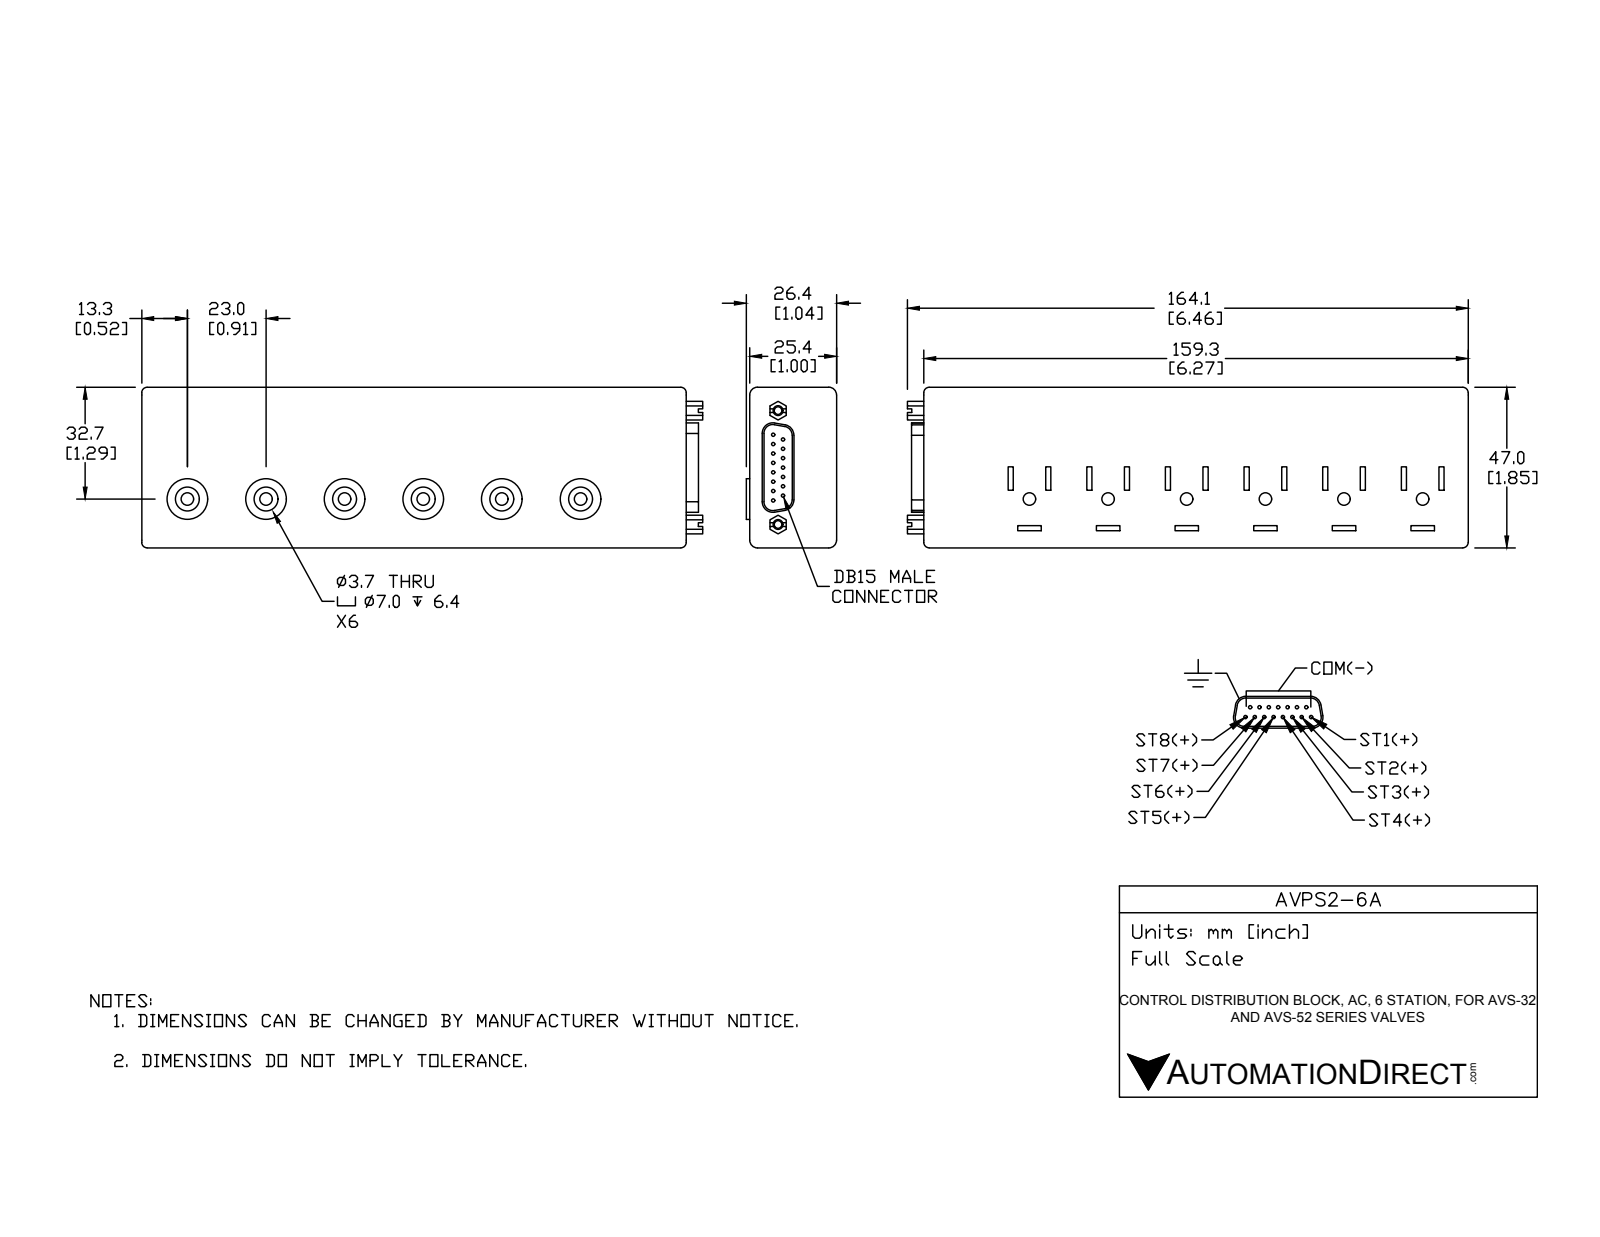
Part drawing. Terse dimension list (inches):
name: AVPS2-6A
written by: SolidWorks 2016 (AUTOMOTIVE_DESIGN)
unit: in
bodies: 1 solid, 265 faces (161 planar, 92 cylindrical, 12 other)
size: 6.461 × 1.85 × 1.04
volume: 11.34 in³; area: 46.49 in²
holes: 6× ⌀0.145, 6× ⌀0.275, 2× ⌀0.089
bosses: 15× ⌀0.039, 6× ⌀0.469
rounds: 8× R0.062, 4× R0.09, 4× R0.102, 4× R0.122
face distances: 1, 1.85, 6.272, 0.059, 0.04, 1.04, 0.906, 0.25, 0.79, 1.812
hole spacings: 0.906, 1.812, 1.812, 2.718, 3.624, 0.906, 1.311, 2.718
